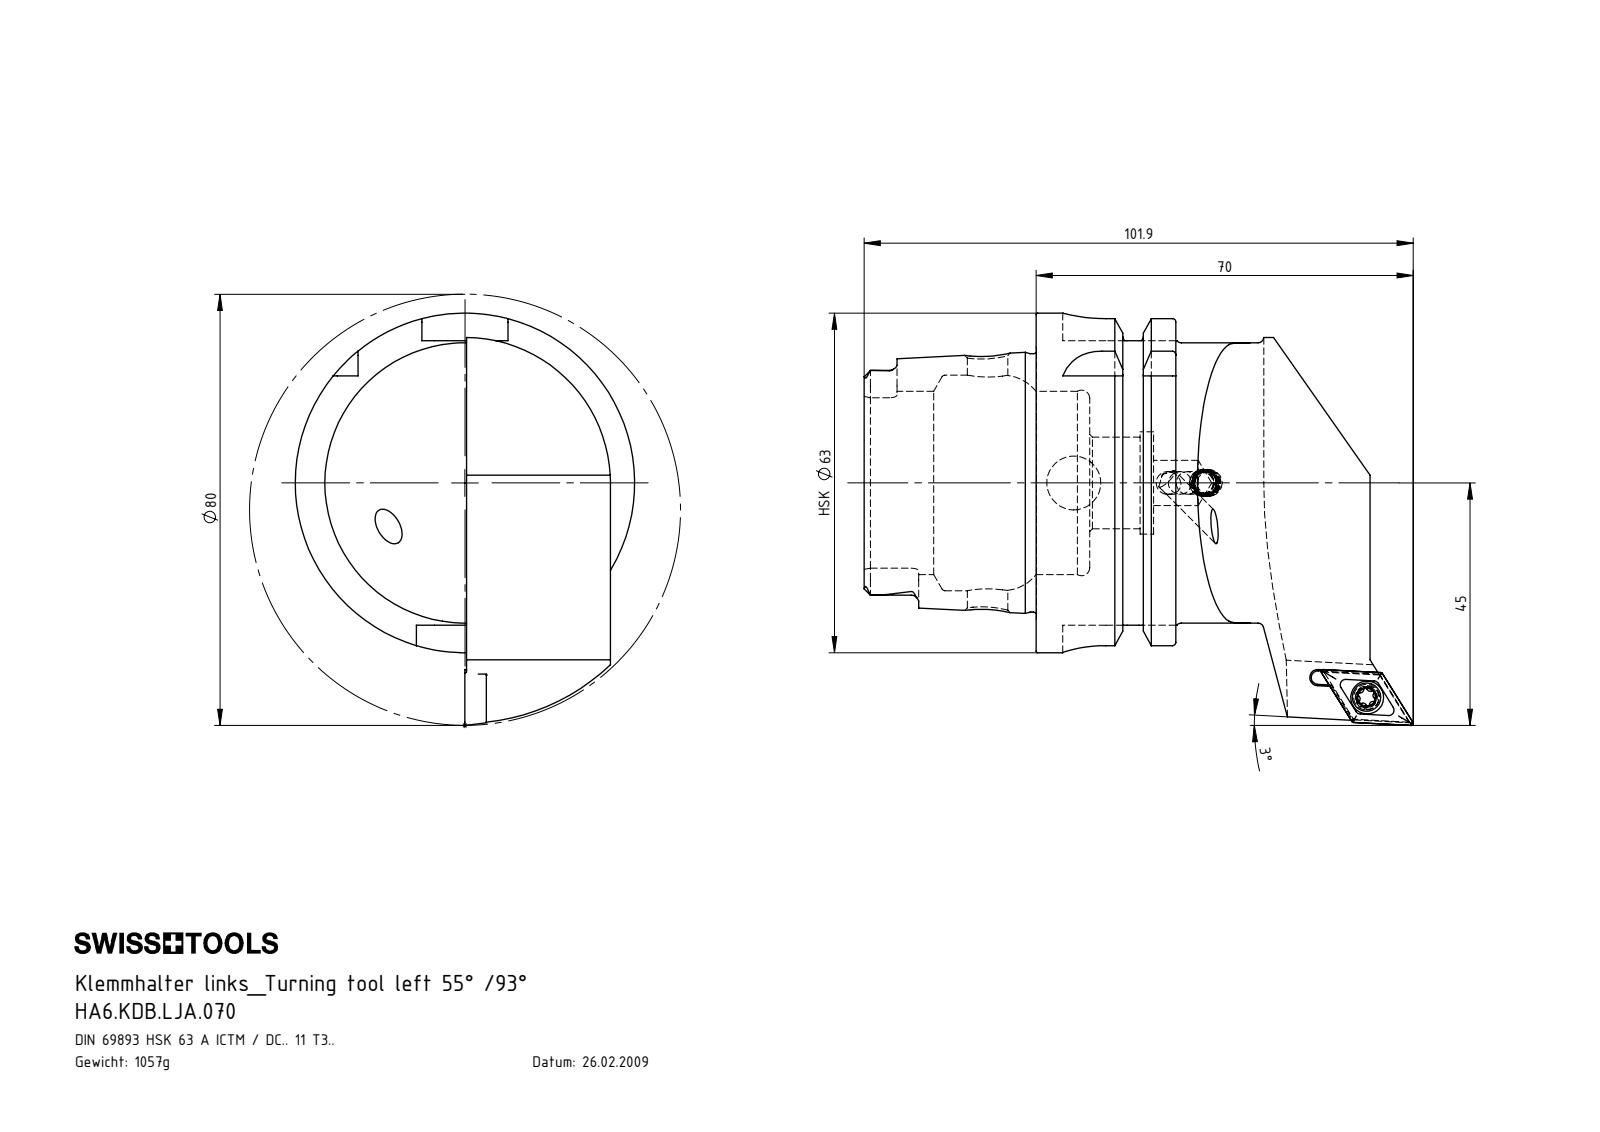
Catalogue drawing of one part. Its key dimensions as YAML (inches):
part_name: "KVT_MB_600_060; DCMT11T304; HA6.KDB.LJA.070; HA6-KDB.LJA.070_C (+1 more)"
step_written_by: "SolidWorks 2017 (AUTOMOTIVE_DESIGN)"
units: inches
bodies: {solids: 5, faces: 237, planar: 79, cylindrical: 60, other: 98}
overall_size: [4.012, 3.012, 2.48]
volume: 7.819
surface_area: 45.92
round_holes:
  - {diameter: 0.197, count: 2}
  - {diameter: 0.13, count: 1}
  - {diameter: 0.173, count: 1}
  - {diameter: 0.24, count: 1}
  - {diameter: 0.295, count: 1}
  - {diameter: 0.331, count: 1}
  - {diameter: 0.394, count: 1}
  - {diameter: 0.669, count: 1}
  - {diameter: 0.748, count: 1}
  - {diameter: 1.339, count: 1}
  - {diameter: 1.575, count: 1}
round_bosses_or_shafts:
  - {diameter: 2.48, count: 1}
  - {diameter: 2.163, count: 1}
  - {diameter: 2.047, count: 1}
  - {diameter: 1.887, count: 1}
  - {diameter: 0.236, count: 1}
  - {diameter: 0.207, count: 1}
  - {diameter: 0.157, count: 1}
partial_cylinders:
  - {radius: 0.013, count: 6}
  - {radius: 0.023, count: 6}
  - {radius: 0.055, count: 6}
  - {radius: 0.315, count: 4}
  - {radius: 0.111, count: 2}
  - {radius: 0.113, count: 2}
  - {radius: 0.049, count: 1}
  - {radius: 0.236, count: 1}
face_to_face_distances: [1.022, 0.63, 0.392, 1.031, 1.256, 1.648, 2.278, 2.079, 0.858, 0.467]
hole_center_spacings: [2.651, 2.656]
